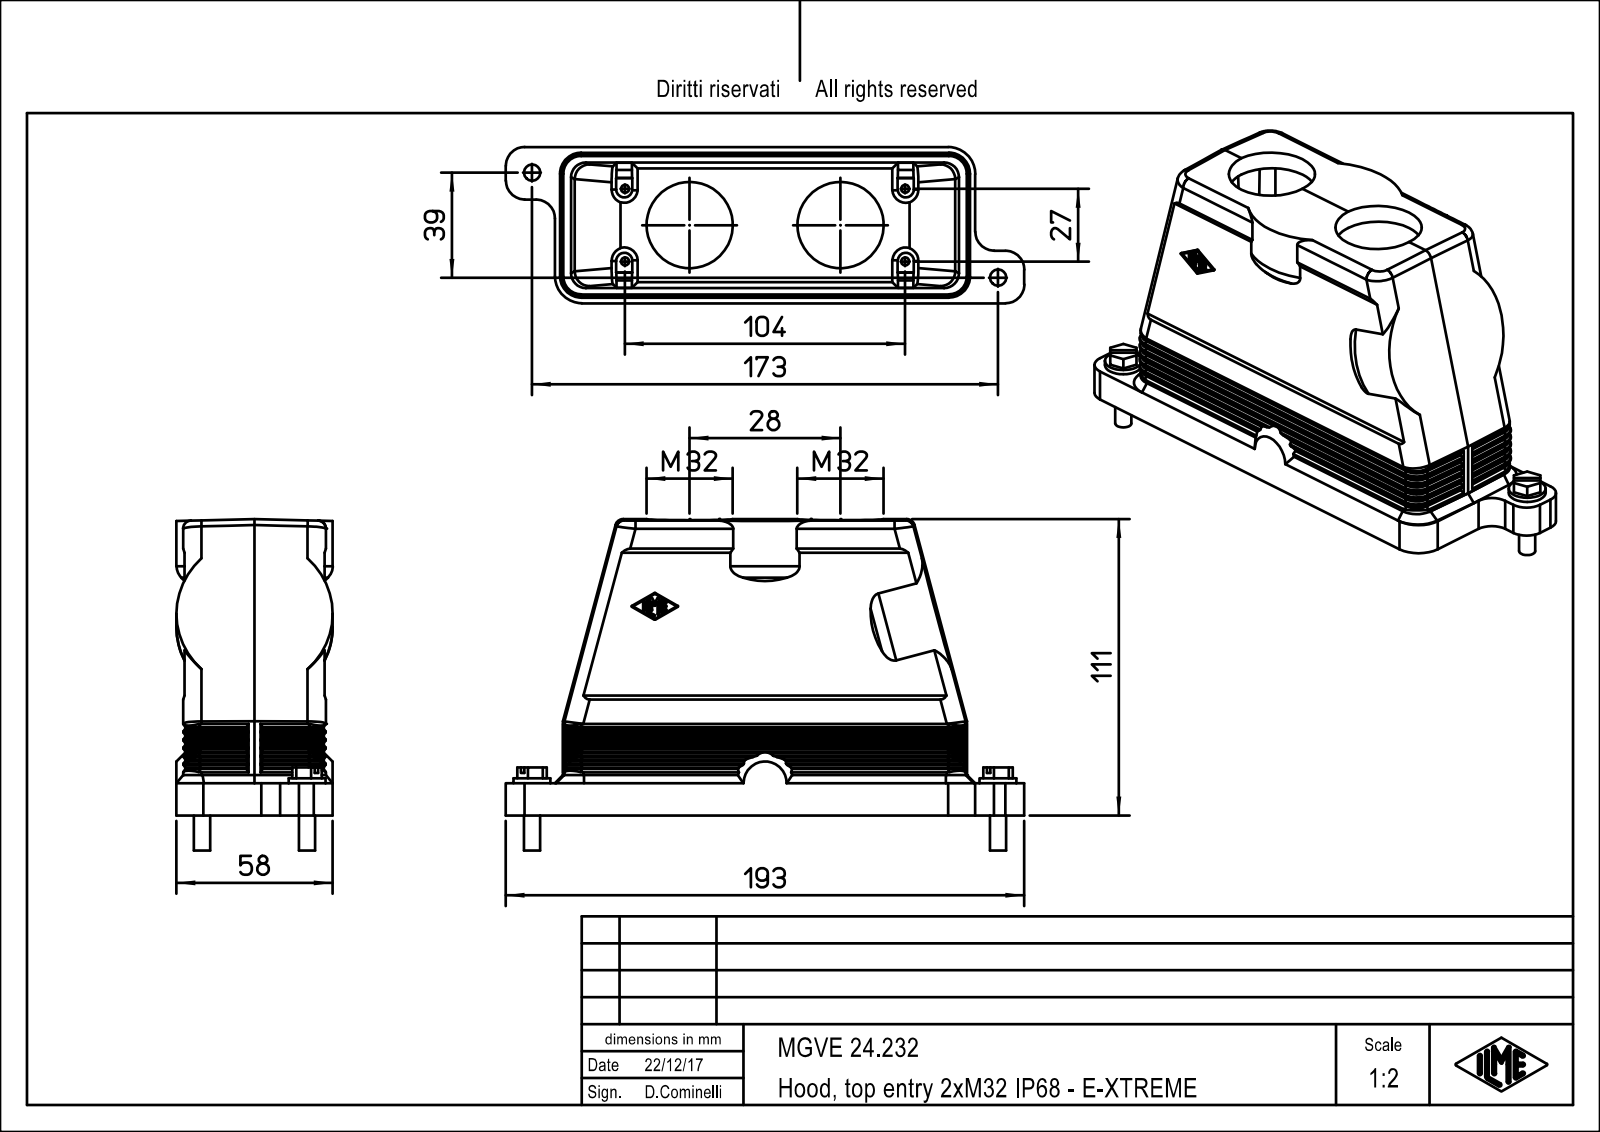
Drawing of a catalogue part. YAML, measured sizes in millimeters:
part_name: "MGVE_24.232"
step_written_by: "PTC Creo Elements/Direct Modeling 19.0E 27-Jun-2016 (C) Parametric Technology GmbH (AUTOMOTIVE_DESIGN)"
units: millimeters
bodies: {solids: 1, faces: 535, planar: 254, cylindrical: 125, other: 156}
overall_size: [192.5, 123, 58]
volume: 211747
surface_area: 98456
round_holes:
  - {diameter: 3, count: 4}
  - {diameter: 32, count: 2}
round_bosses_or_shafts:
  - {diameter: 13.7, count: 2}
  - {diameter: 6, count: 2}
partial_cylinders:
  - {radius: 7, count: 62}
  - {radius: 0.33, count: 15}
  - {radius: 5.5, count: 8}
  - {radius: 7.3, count: 4}
  - {radius: 0.17, count: 2}
  - {radius: 10, count: 2}
  - {radius: 29, count: 2}
  - {radius: 0.17, count: 1}
face_to_face_distances: [52, 3, 55, 0.5, 2.5, 55.5, 52.5, 3.33, 104.5, 58]
hole_center_spacings: [27.54, 81.13, 27, 104, 107.45, 56]
